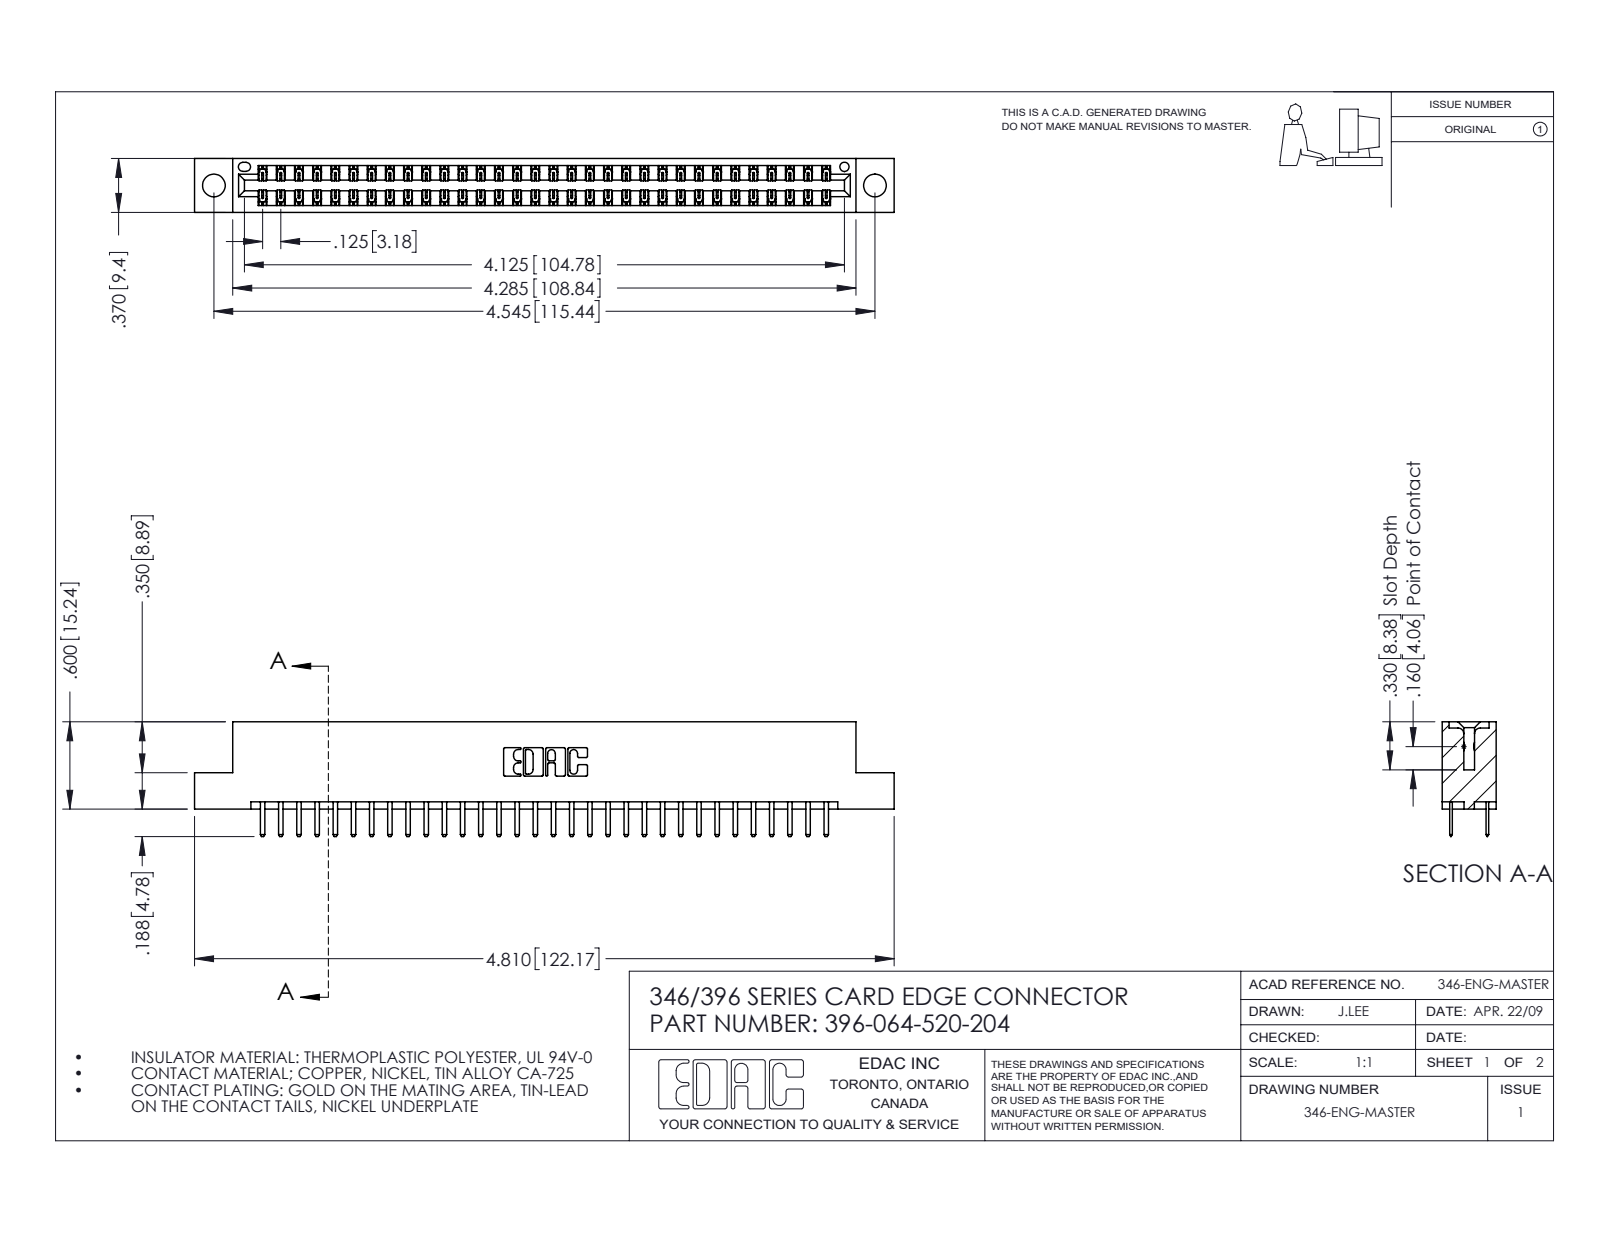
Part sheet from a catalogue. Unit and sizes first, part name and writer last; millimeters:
Units: millimetres
Overall size (bounding box): 122.2 × 20 × 9.4
Round holes (diameter × count): ⌀4 ×2, ⌀1.6 ×1
Partial cylindrical surfaces — rounded edges, fillets, slot ends (radius × count): R0.2 ×96, R0.3 ×68, R0.3 ×22, R0.2 ×6, R0.8 ×6, R0.7 ×3, R0.4 ×2, R0.6 ×2
Main face-to-face distances: 1.2, 8.2, 6.4, 9.4, 7, 1.8, 7.6, 0.6, 3.8, 5.6
Hole centre spacings: 6.2, 110.2, 115.4
Volume: 11 700 mm³ · Surface area: 15 700 mm²
Bodies: 65 solids, 3706 faces (2444 planar, 1262 cylindrical, 0 other)
Part name (STEP PRODUCT): 345-292-001_345-293-120; 346 Part_Flush Mounting Lugs - 0.156 Dia-TH; 396-064-520-204
STEP written by: SolidWorks 2016 (CONFIG_CONTROL_DESIGN)
